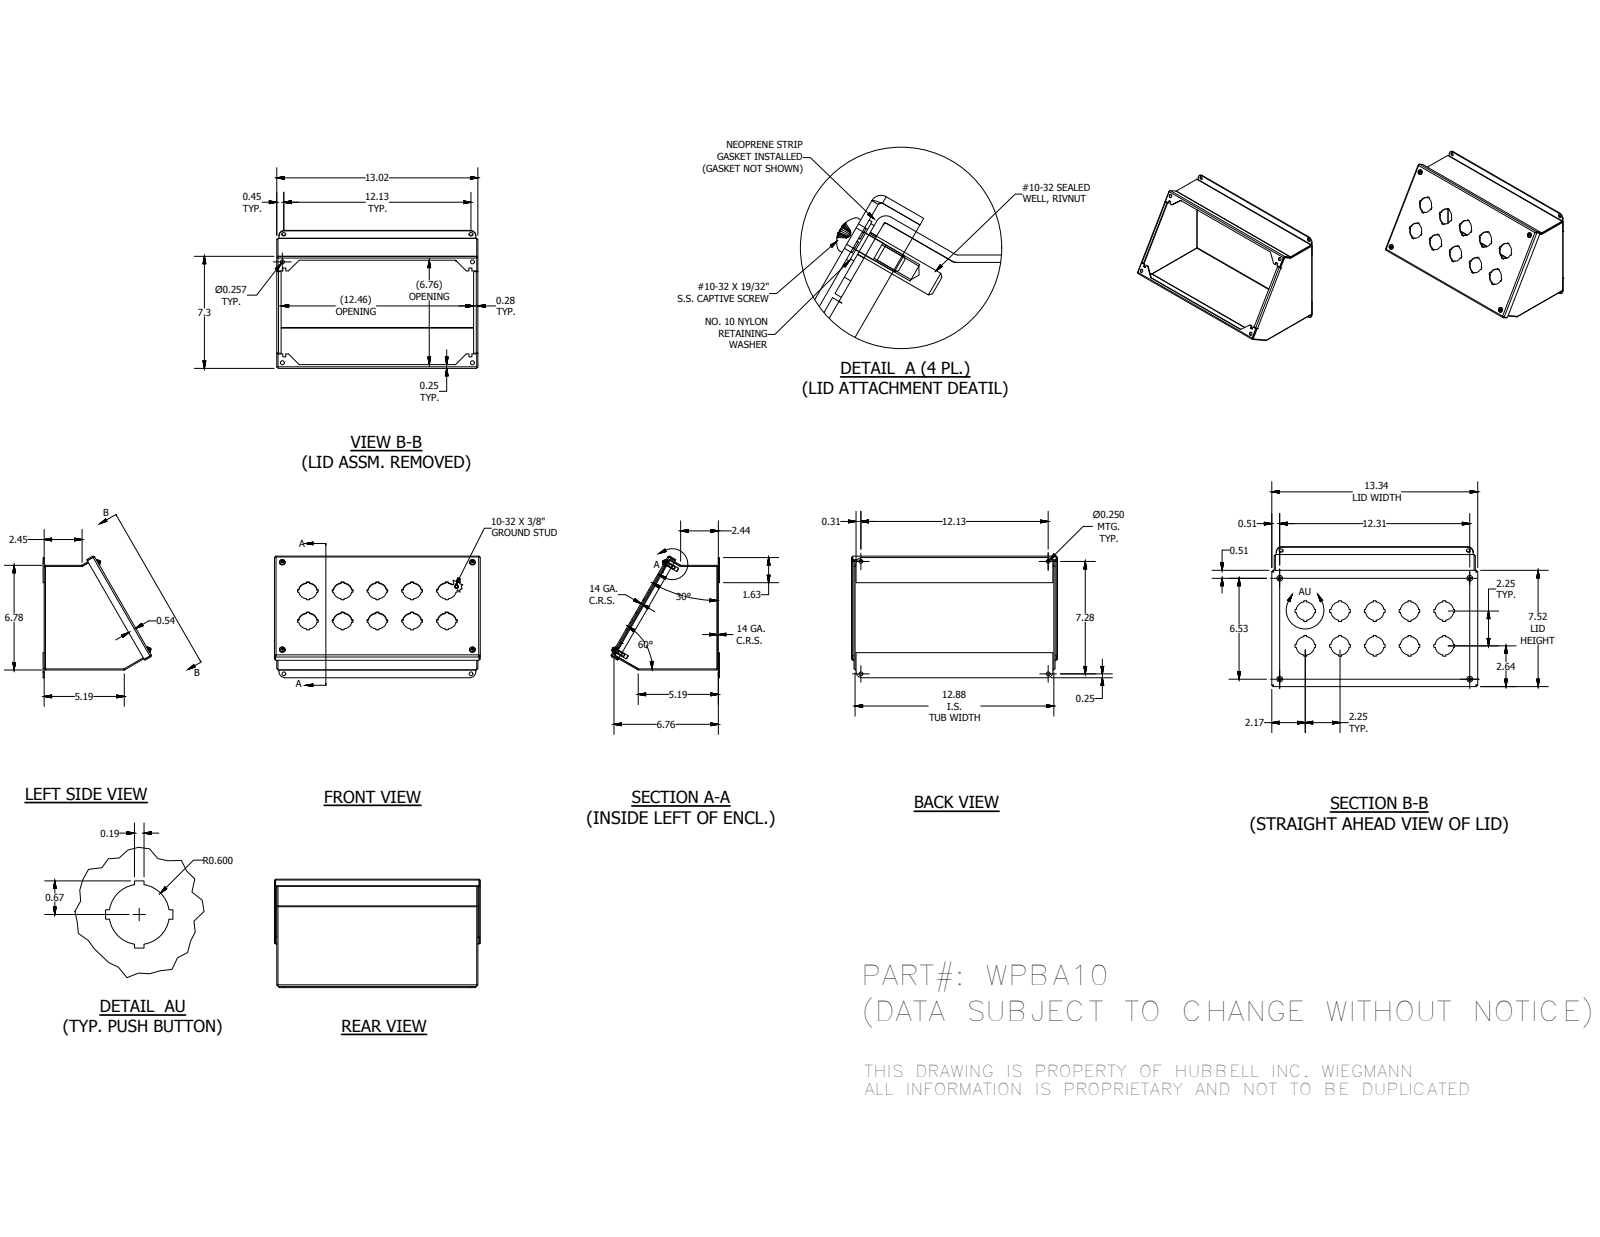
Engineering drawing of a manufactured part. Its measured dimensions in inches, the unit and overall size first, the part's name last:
Units: inches
Overall size (bounding box): 13.337 × 7.873 × 7.016
Round holes (diameter × count): ⌀1.2 ×10, ⌀0.156 ×4, ⌀0.196 ×4, ⌀0.25 ×4, ⌀0.257 ×4, ⌀0.278 ×4, ⌀0.281 ×4
Round bosses / shafts (diameter × count): ⌀0.19 ×5, ⌀0.453 ×4, ⌀0.406 ×4, ⌀0.373 ×4, ⌀0.248 ×4, ⌀0.25 ×1
Partial cylindrical surfaces — rounded edges, fillets, slot ends (radius × count): R0.031 ×12, R0.105 ×12, R0.089 ×4, R0.375 ×4
Main face-to-face distances: 0.074, 6.706, 0.074, 0.148, 12.949, 12.949, 13.023, 12.875, 6.632, 6.78
Hole centre spacings: 2.25, 3.182, 4.5, 5.031, 2.25, 2.694, 4.677, 6.512
Volume: 32.91 in³ · Surface area: 912 in²
Bodies: 19 solids, 640 faces (411 planar, 130 cylindrical, 99 other)
Part name (STEP PRODUCT): WPBA10BKP; WPBA2ROWEWPR; WPBA2ROWEWPL; 34984 (+6 more)
STEP written by: Autodesk Inventor 2014 (AUTOMOTIVE_DESIGN)
